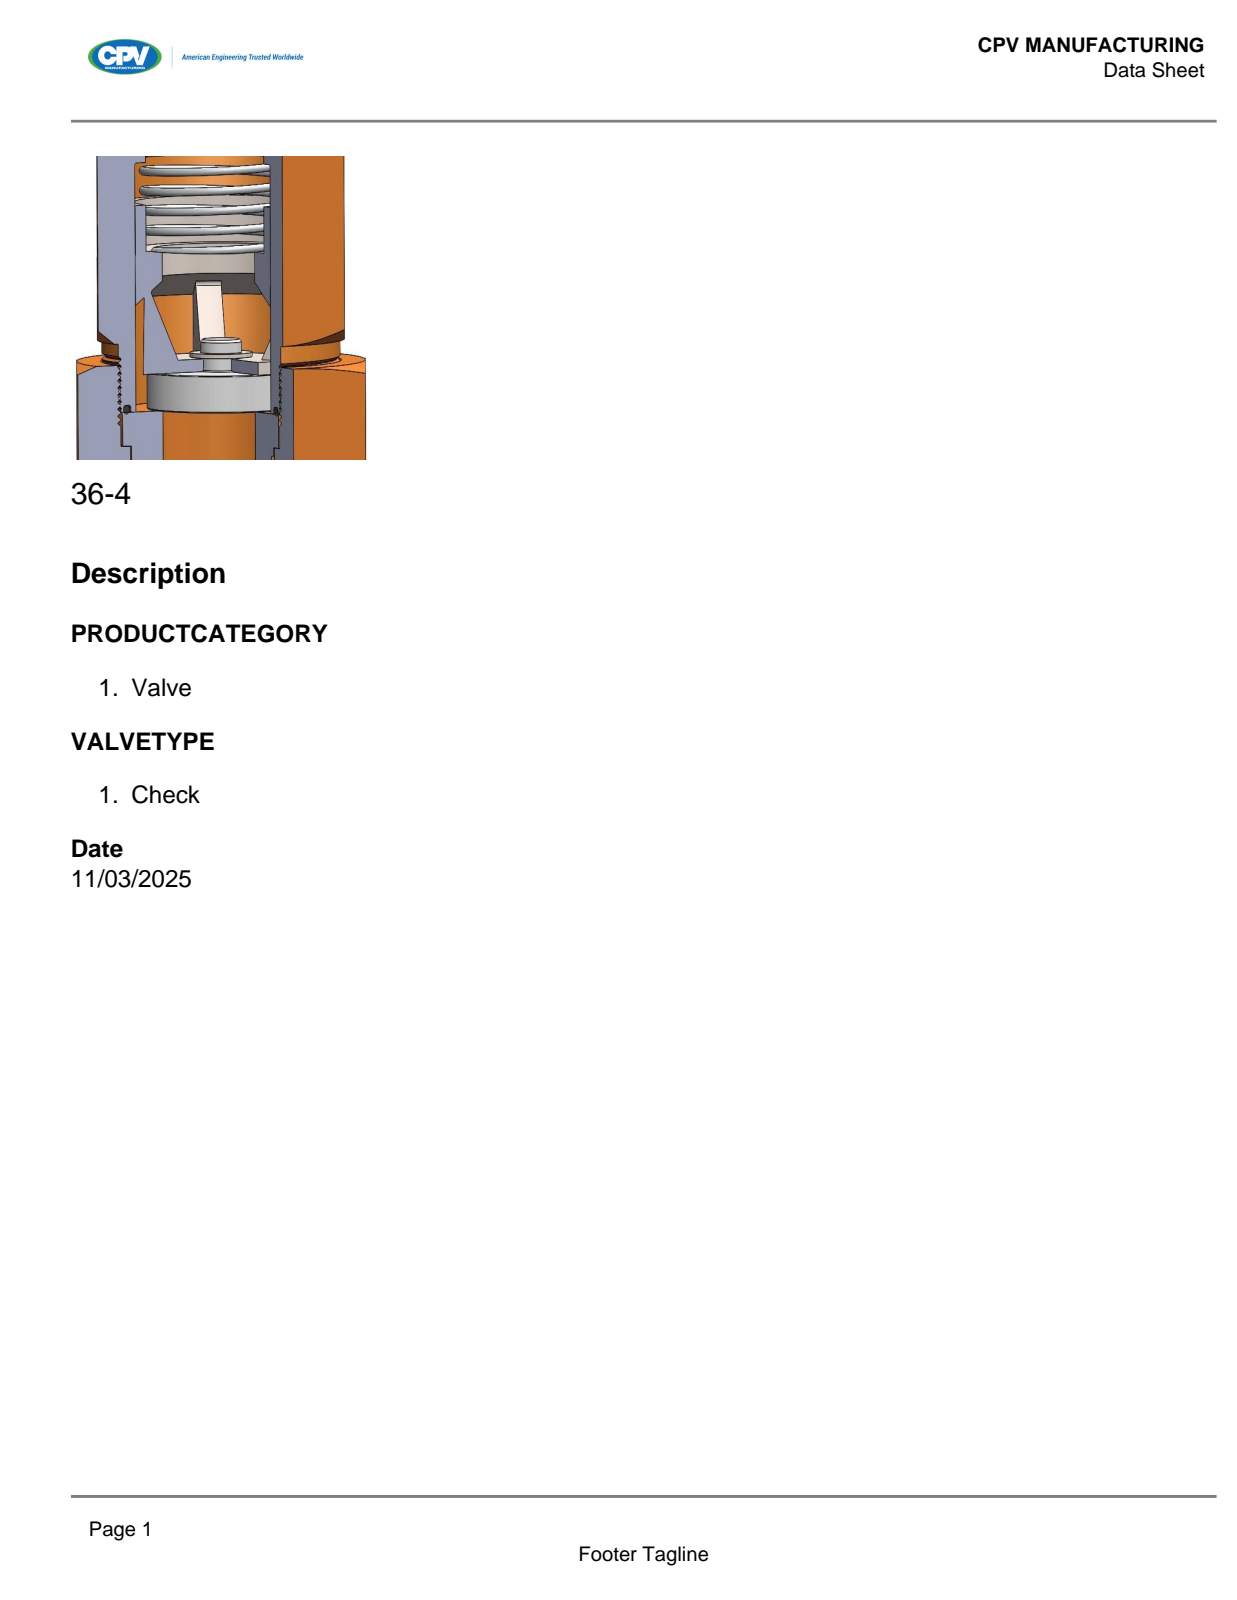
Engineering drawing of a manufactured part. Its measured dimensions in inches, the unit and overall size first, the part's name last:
Units: inches
Overall size (bounding box): 4 × 2.748 × 2.38
Round holes (diameter × count): ⌀0.75 ×1
Round bosses / shafts (diameter × count): ⌀1.87 ×1, ⌀1.75 ×1
Partial cylindrical surfaces — rounded edges, fillets, slot ends (radius × count): R0.775 ×1
Main face-to-face distances: 2.19, 0.19, 2.38, 2, 0.445, 0.255, 1.935, 1.745, 2.93, 0.94
Volume: 11.65 in³ · Surface area: 43.04 in²
Bodies: 1 solid, 110 faces (29 planar, 45 cylindrical, 36 other)
Part name (STEP PRODUCT): 36-4
STEP written by: SolidWorks 2018 (AUTOMOTIVE_DESIGN)
